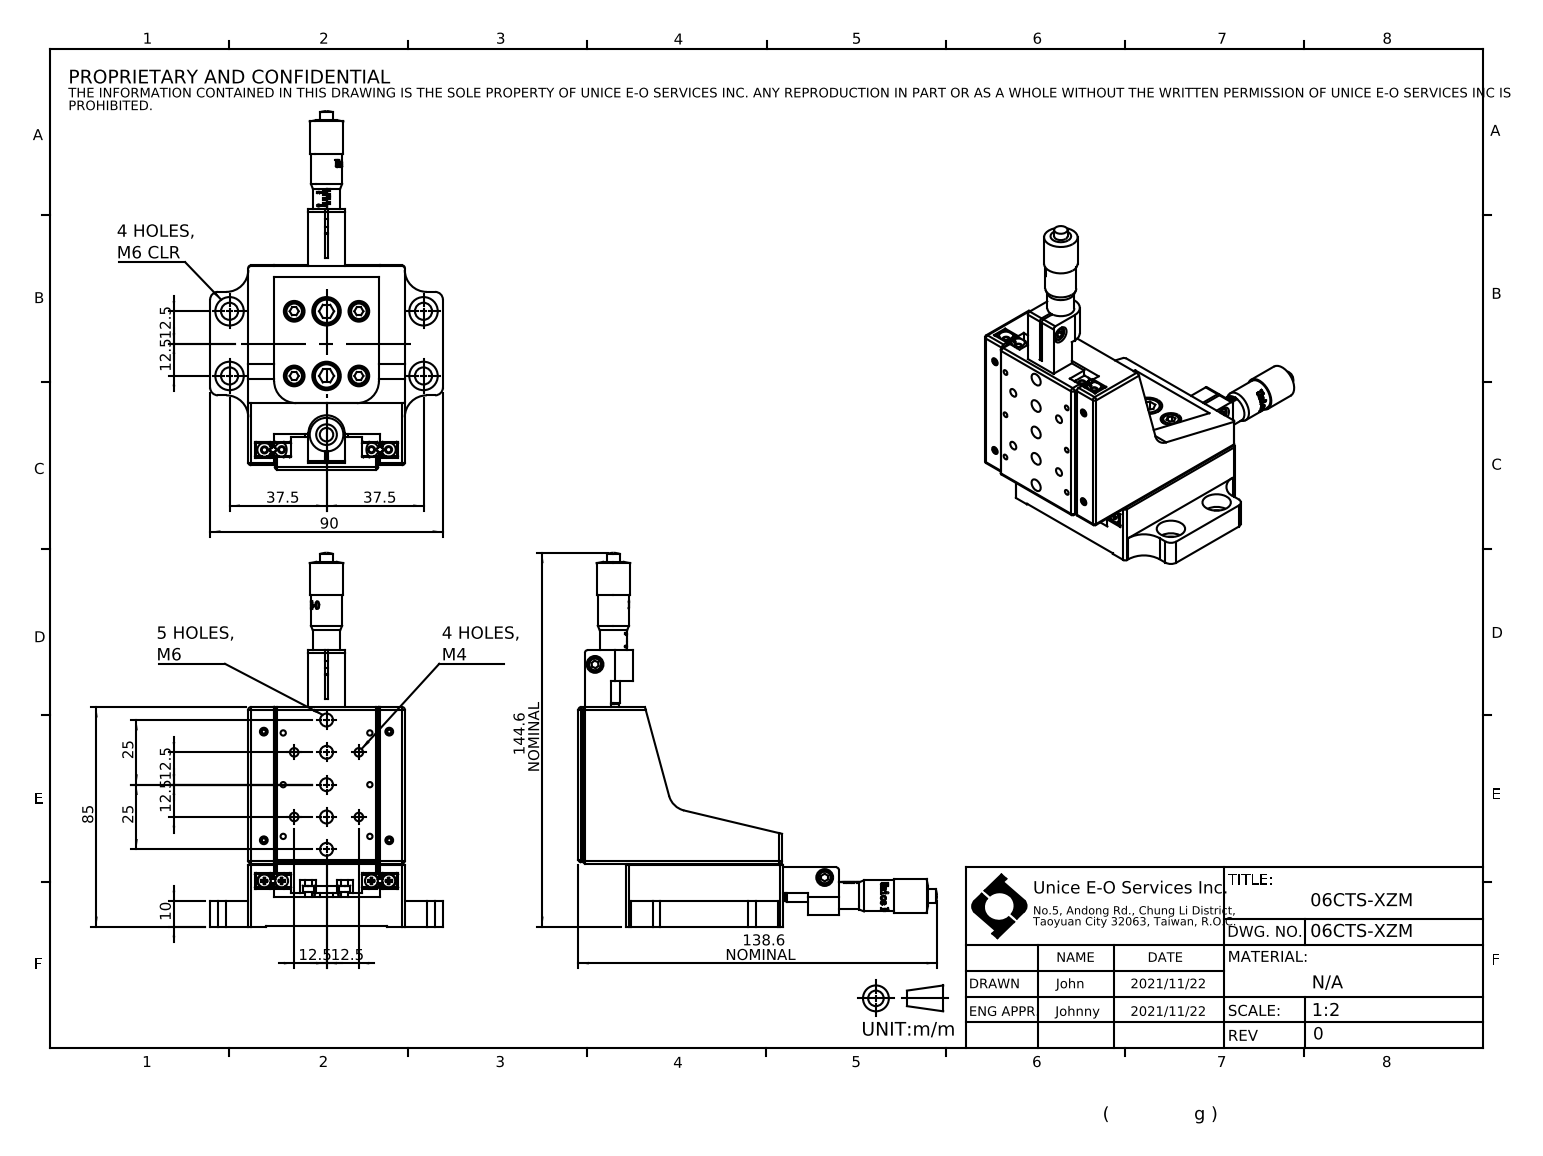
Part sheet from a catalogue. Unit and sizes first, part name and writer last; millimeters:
Units: millimetres
Overall size (bounding box): 144.65 × 138.6 × 90
Round holes (diameter × count): ⌀2.05 ×10, ⌀8 ×6, ⌀11 ×6, ⌀5 ×5, ⌀3.3 ×4, ⌀6.6 ×4, ⌀2.5 ×2, ⌀6.5 ×2, ⌀9.5 ×2, ⌀10.6 ×1
Round bosses / shafts (diameter × count): ⌀5 ×6, ⌀4.5 ×4, ⌀13 ×2, ⌀12 ×2, ⌀10.5 ×2, ⌀7 ×2, ⌀5.2 ×2, ⌀4 ×2
Partial cylindrical surfaces — rounded edges, fillets, slot ends (radius × count): R1 ×31, R8.5 ×6, R3 ×4, R5.98 ×2, R7 ×2, R8 ×1
Main face-to-face distances: 14, 60.5, 11.5, 13, 12.5, 25.5, 6, 3, 12, 1.5
Hole centre spacings: 25, 12.5, 17.68, 27.95, 35.36, 37.5, 50, 8.62
Bodies: 0 solids, 854 faces (510 planar, 230 cylindrical, 114 other)
Part name (STEP PRODUCT): 06CTS-XZM
STEP written by: SolidWorks 2021 (CONFIG_CONTROL_DESIGN)
